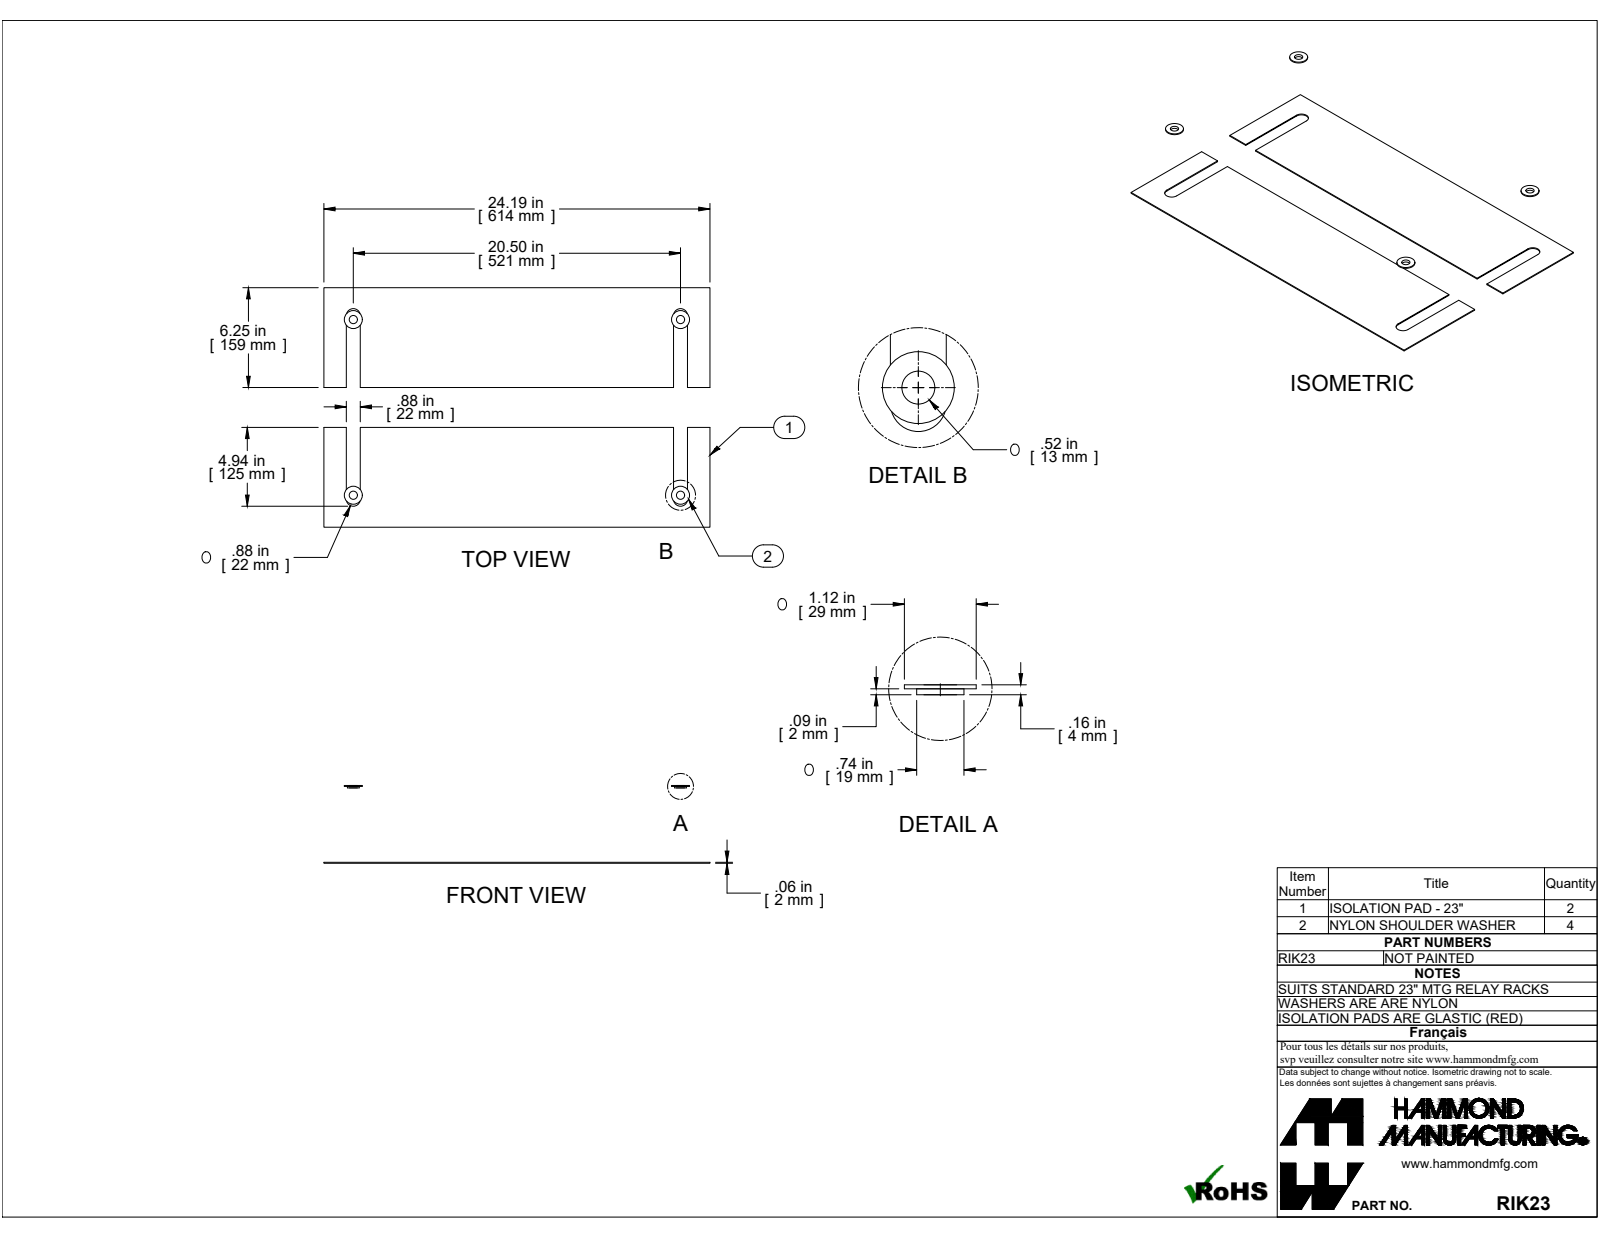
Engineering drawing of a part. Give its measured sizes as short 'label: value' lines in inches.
name: COM57164-23
written by: ST-DEVELOPER v16.7 (TECHNICAL_DATA_PACKAGING)
unit: in
bodies: 1 solid, 14 faces (12 planar, 2 cylindrical, 0 other)
size: 24.188 × 6.25 × 0.063
volume: 8.919 in³; area: 290.4 in²
rounds: 2× R0.437
face distances: 0.063, 6.25, 1.406, 2.281, 21.907, 22.782, 0.875, 20.5, 24.188, 21.376
